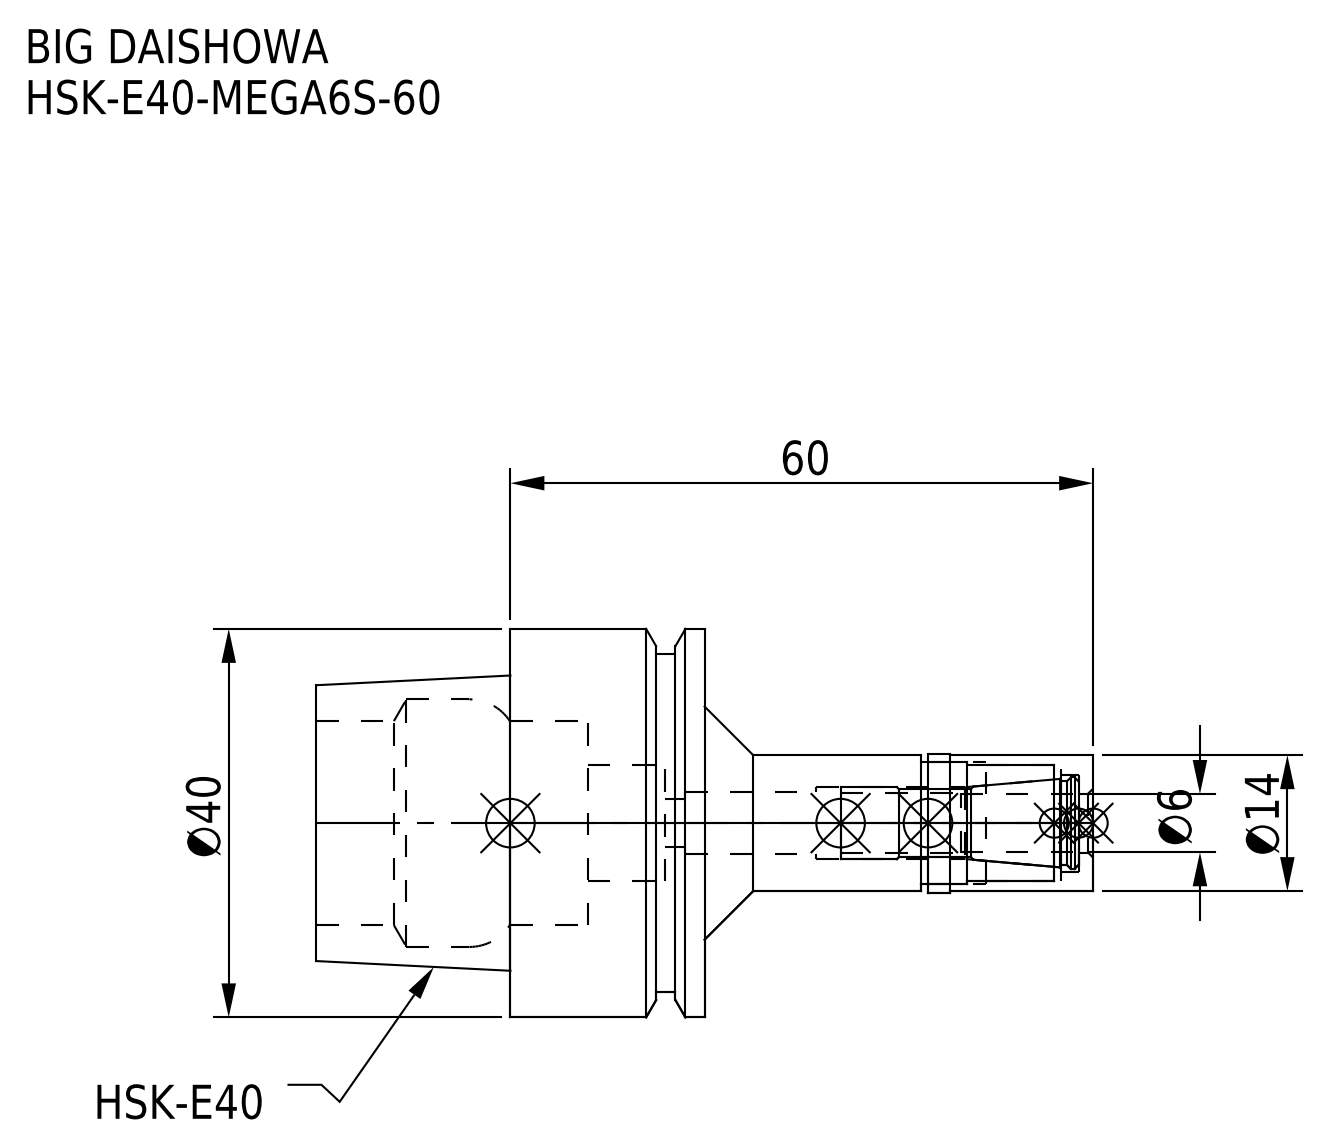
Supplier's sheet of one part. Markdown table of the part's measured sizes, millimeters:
| quantity | value |
| --- | --- |
| part name | MGN6S_1.stp; HE40MS06060-060_ASM.stp; DXF_TEMP_ASSY_ASM_4_ASM.stp; HSK-E40-MEGA6S-60_1.stp (+3 more) |
| STEP written by | SolidWorks 2019 (CONFIG_CONTROL_DESIGN) |
| units | millimeters |
| bodies | 2 solids, 74 faces (18 planar, 40 cylindrical, 16 other) |
| overall size | 80 × 40 × 40 |
| volume | 30 583 mm³ |
| surface area | 13 473 mm² |
| round holes (diameter × count) | 5 × 1, 6.1 × 1, 6.4 × 1, 7.4 × 1, 10 × 1, 12 × 1, 12.5 × 1, 21 × 1, 25.5 × 1 |
| round bosses / shafts (diameter × count) | 40 × 1, 34.8 × 1, 14.3 × 1, 14 × 1 |
| main face-to-face distances | 20, 40, 12.05, 7.95, 27.95, 17, 43, 2, 52.05, 60 |
